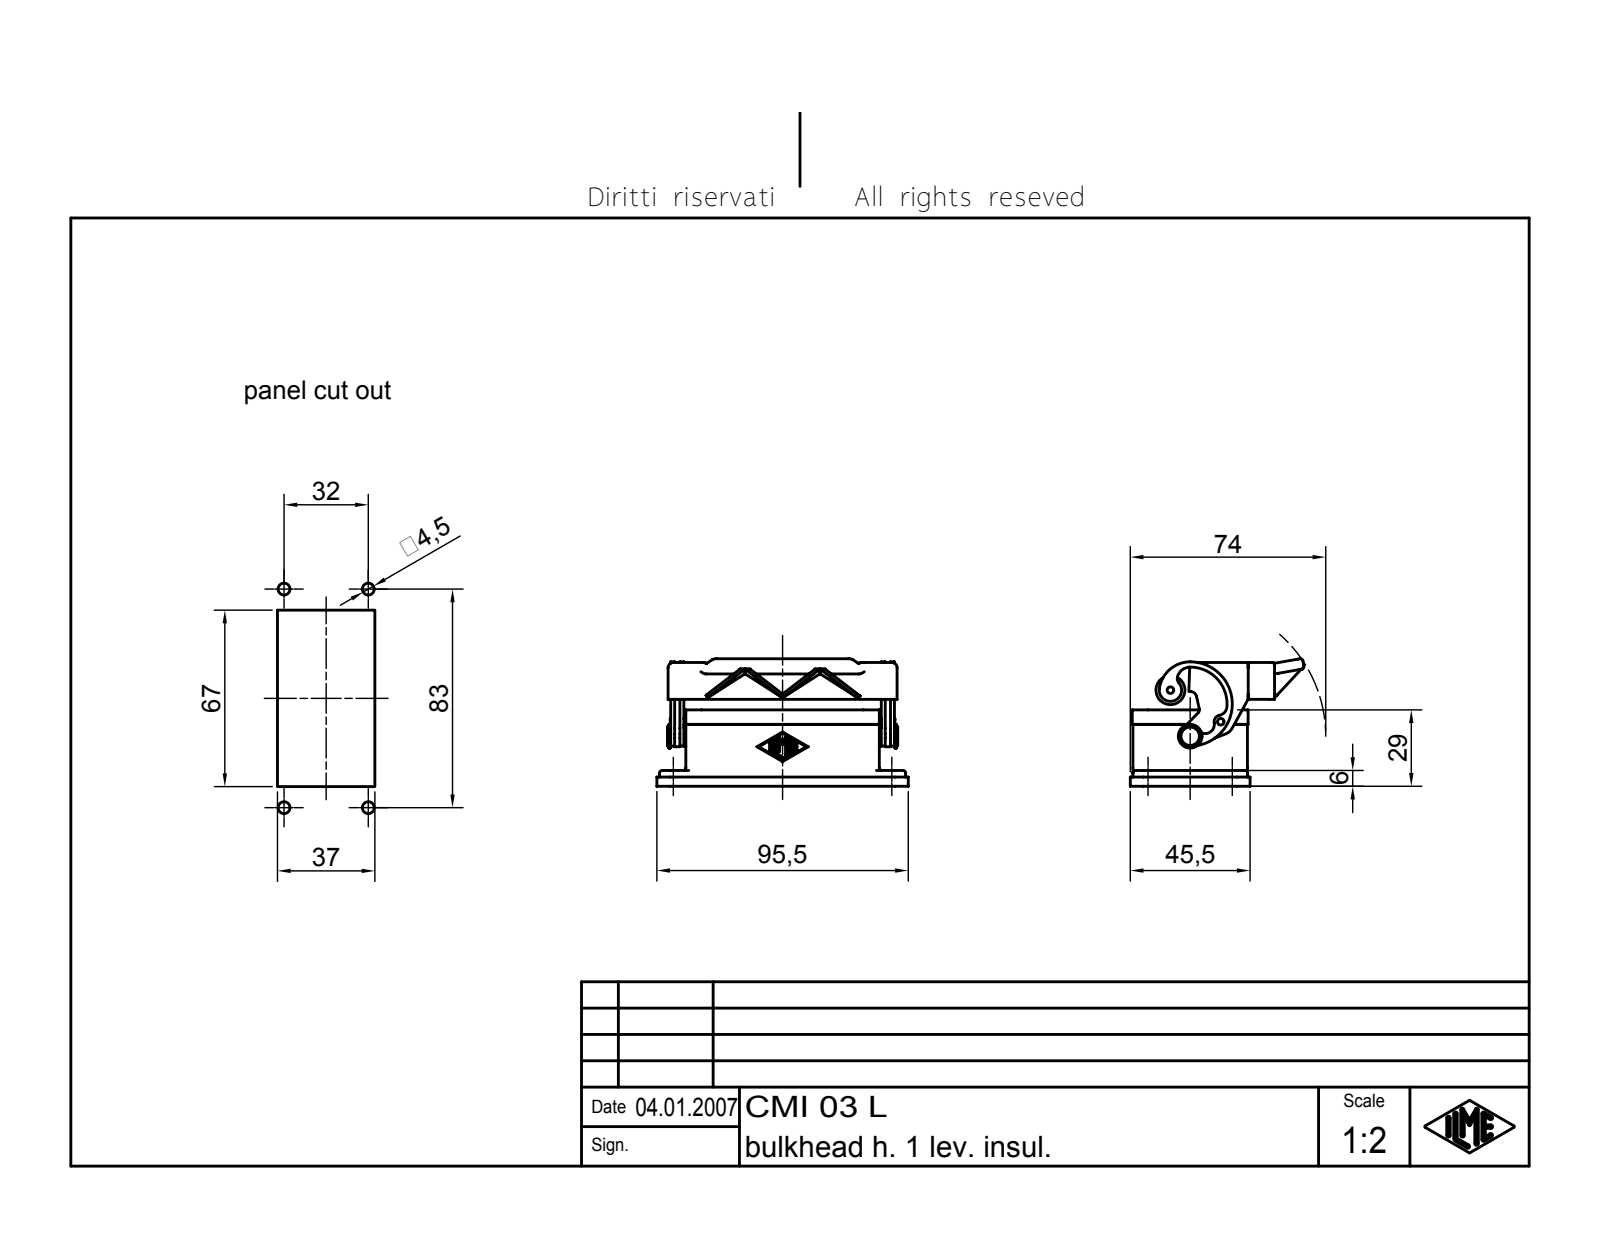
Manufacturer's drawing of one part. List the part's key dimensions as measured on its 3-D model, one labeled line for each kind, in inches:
Part name (STEP PRODUCT): CMI 03 L
STEP written by: Autodesk Inventor 7 (AUTOMOTIVE_DESIGN)
Units: inches
Bodies: 4 solids, 468 faces (152 planar, 152 cylindrical, 164 other)
Overall size (bounding box): 3.76 × 2.596 × 1.906
Volume: 2.523 in³ · Surface area: 45.15 in²
Round holes (diameter × count): ⌀0.173 ×4, ⌀0.177 ×4, ⌀0.079 ×1
Round bosses / shafts (diameter × count): ⌀0.433 ×1, ⌀0.354 ×1, ⌀0.197 ×1, ⌀0.118 ×1, ⌀0.098 ×1
Partial cylindrical surfaces — rounded edges, fillets, slot ends (radius × count): R0.015 ×14, R0.039 ×13, R0.079 ×12, R0.236 ×8, R0.098 ×7, R0.197 ×6, R0.157 ×5, R0.118 ×4
Main face-to-face distances: 0.118, 0.157, 1.594, 0.03, 0.039, 0.925, 1.713, 1.604, 2.776, 1.476
Hole centre spacings: 1.26, 3.268, 3.502
